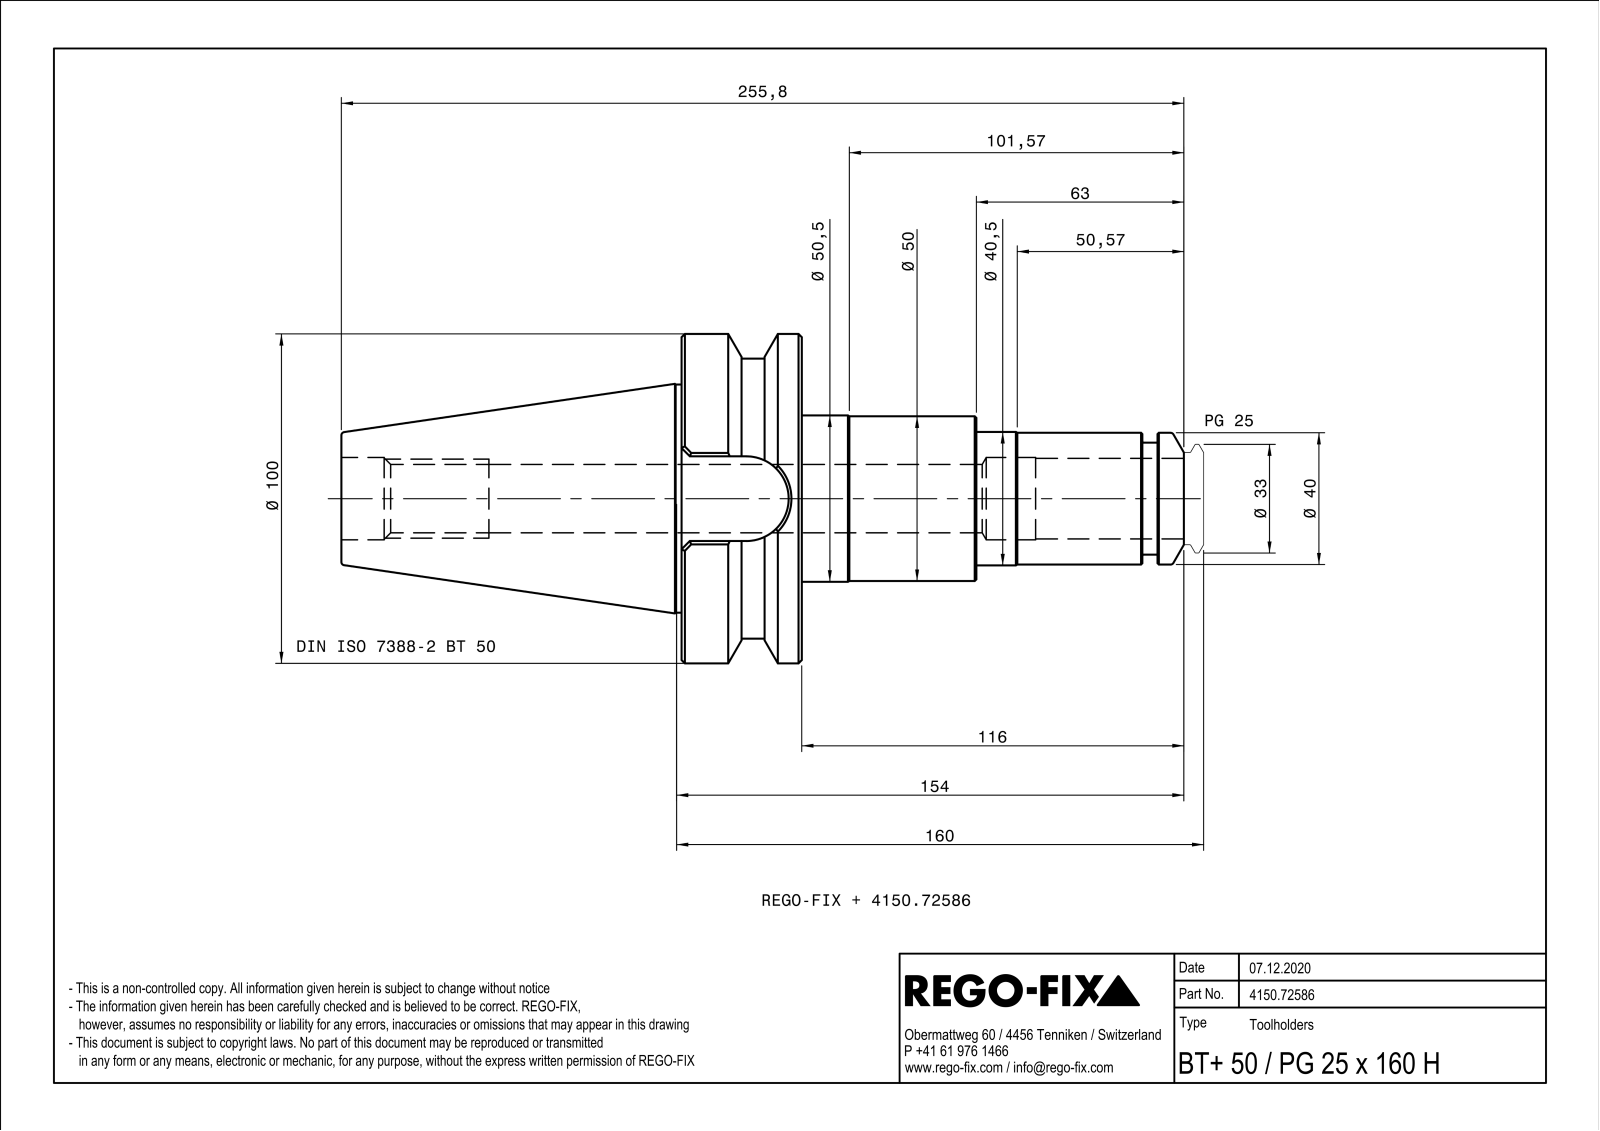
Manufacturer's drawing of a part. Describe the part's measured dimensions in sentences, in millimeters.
The part is named "NOCUT". Its 3-D file was written by "SIEMENS PLM Software Solid Edge ST10 (AUTOMOTIVE_DESIGN)". It is 1 solid with 116 faces: 28 planar, 30 cylindrical and 58 other. Overall it measures 255.8 by 100 by 100 millimeters. Its volume is 581 762 cubic millimeters and its surface area 78 259 square millimeters. Round holes: 1 of diameter 20.75, 1 of diameter 25. Round bosses or shafts: 1 of diameter 100, 1 of diameter 85, 1 of diameter 69.25, 1 of diameter 50.5, 1 of diameter 50, 1 of diameter 40.5, 1 of diameter 40, 1 of diameter 34. Partial cylindrical surfaces (rounded edges, fillets, slot ends): 8 of radius 0.5, 1 of radius 12.85. The main face-to-face distances are 36.5, 70.7, 139.8, 103.3, 53, 89.5, 192.8, 25.7, 50.4, 103.4.
